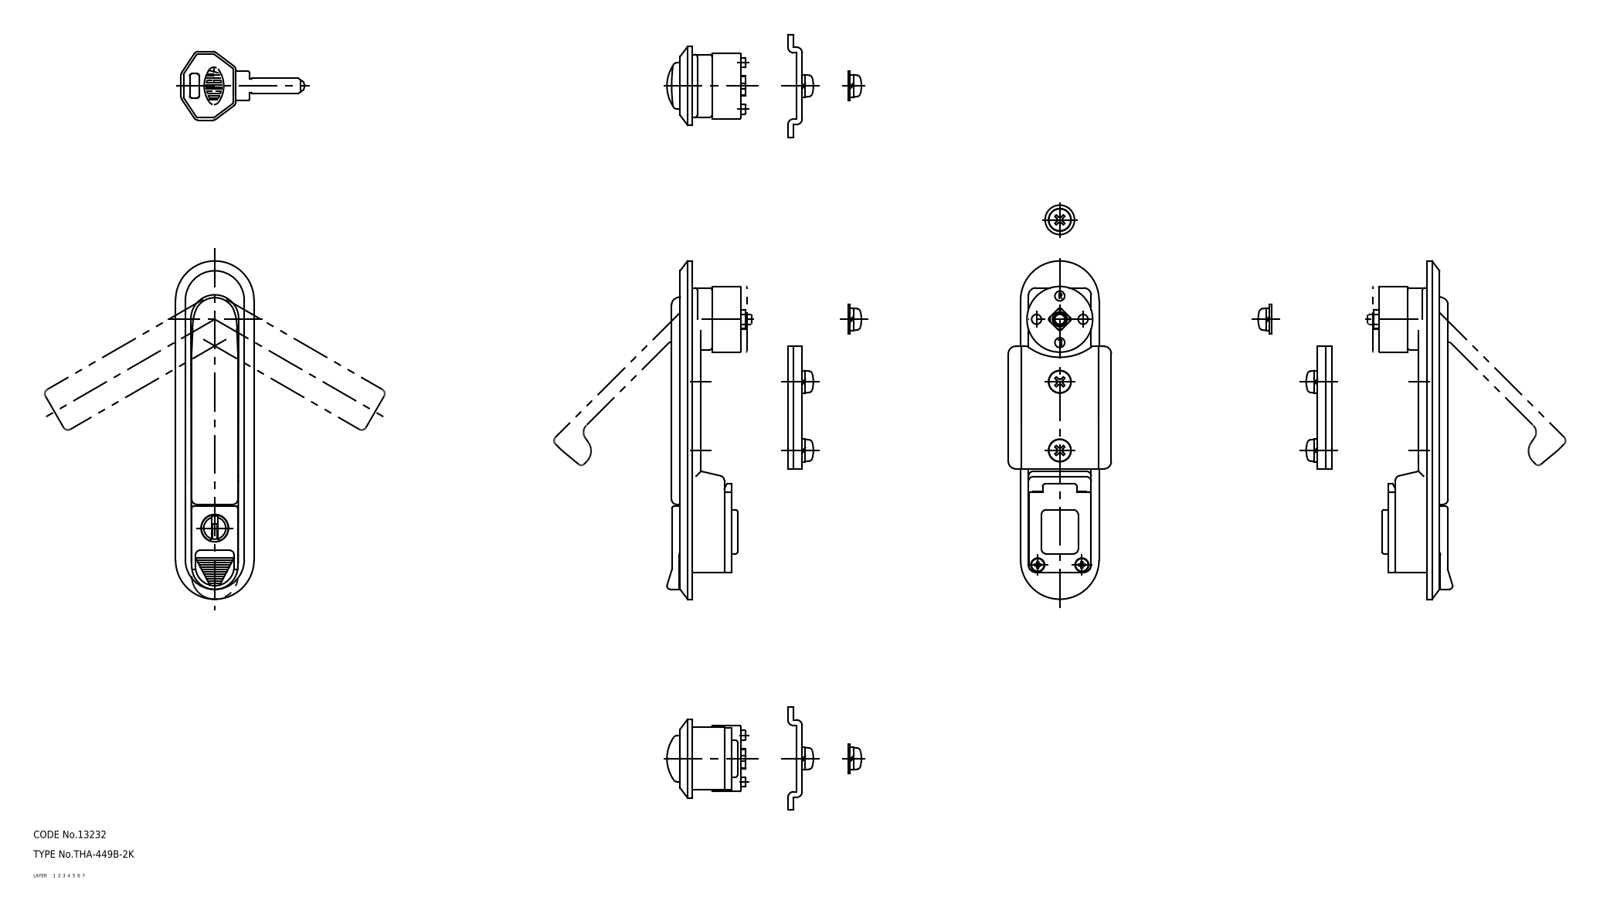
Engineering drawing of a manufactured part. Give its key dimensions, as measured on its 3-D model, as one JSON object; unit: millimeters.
{"part_name": "screw_A; lock; shaft; screw_B (+7 more)", "step_written_by": "CADfix (AUTOMOTIVE_DESIGN)", "units": "millimeters", "bodies": {"solids": 11, "faces": 598, "planar": 0, "cylindrical": 0, "other": 598}, "overall_size": [138, 108.37, 42], "volume_mm3": 49267, "surface_area_mm2": 37352}
